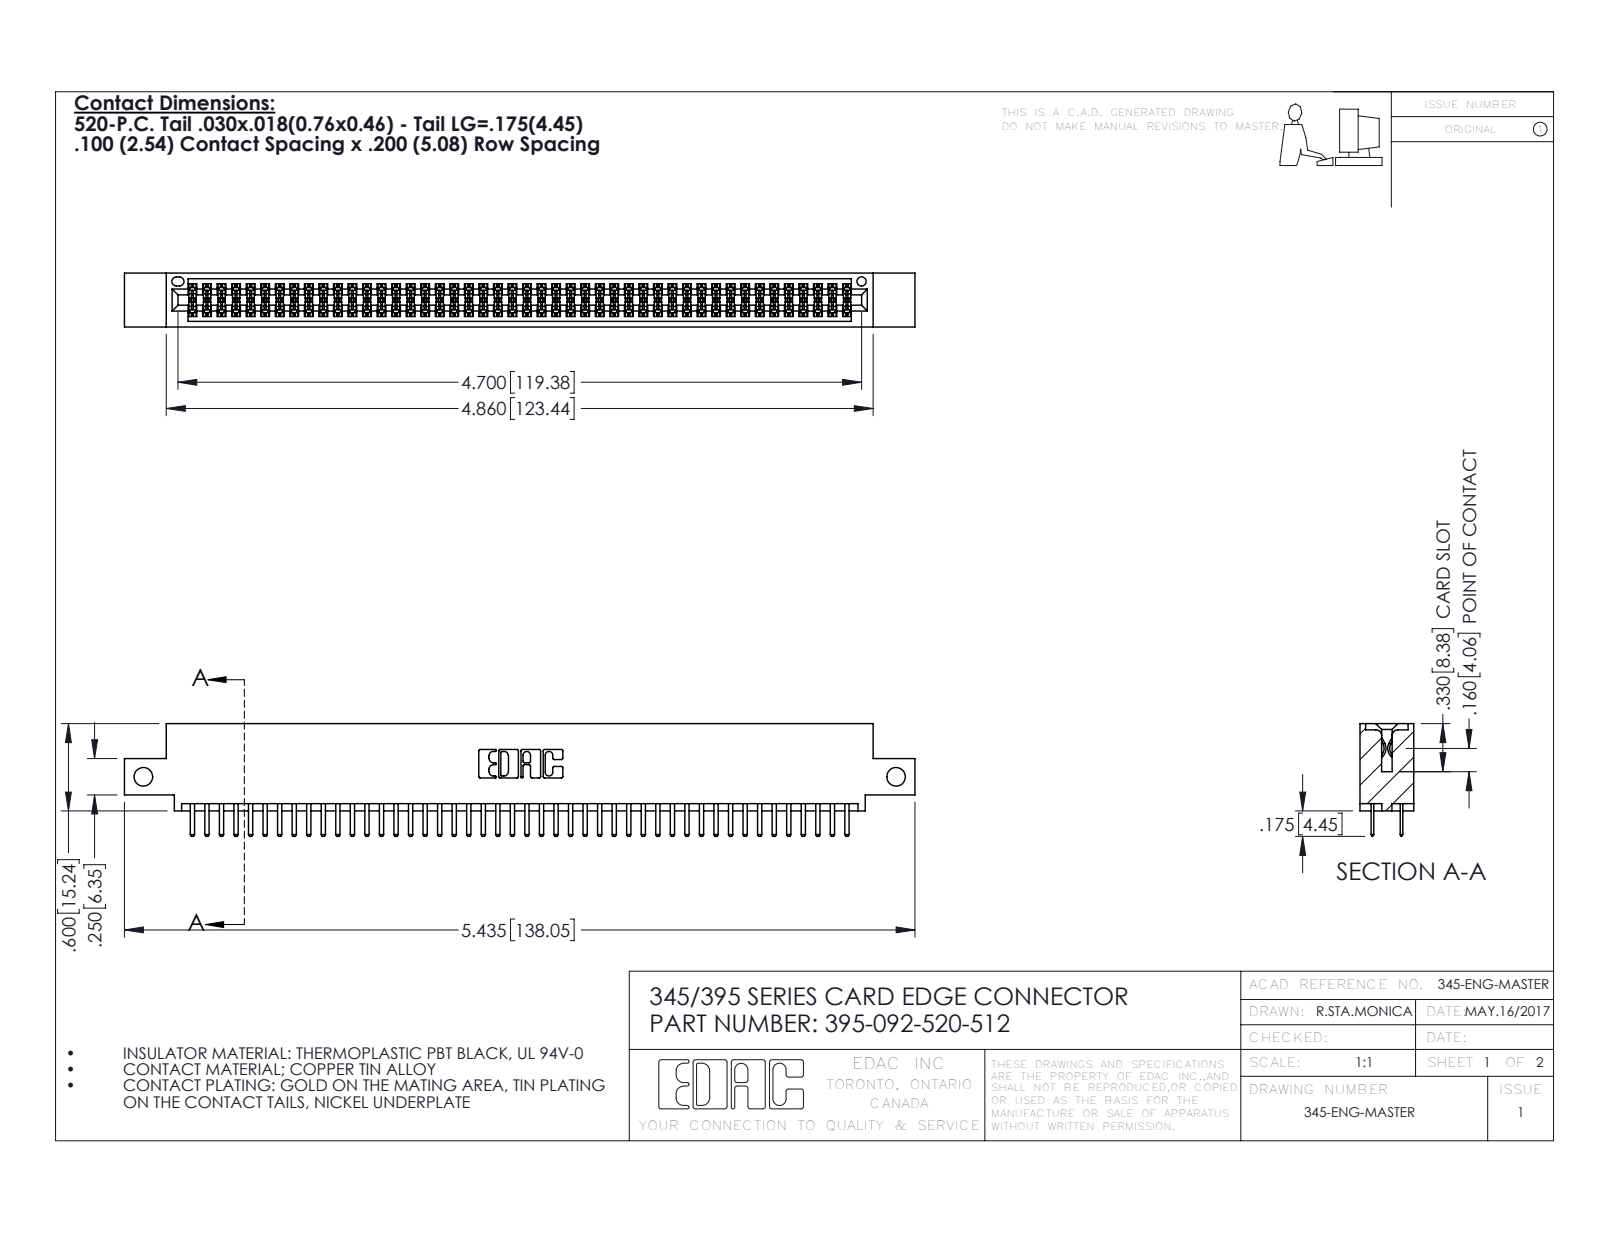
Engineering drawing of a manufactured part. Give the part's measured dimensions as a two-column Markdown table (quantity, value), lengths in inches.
| quantity | value |
| --- | --- |
| part name | 345 Part_0.110 Offset - Side Mount; 345-292-001_345-293-120; 395-092-520-512 |
| STEP written by | SolidWorks 2016 (CONFIG_CONTROL_DESIGN) |
| units | inches |
| bodies | 93 solids, 5098 faces (3304 planar, 1794 cylindrical, 0 other) |
| overall size | 5.435 × 0.775 × 0.37 |
| volume | 0.808 in³ |
| surface area | 30.27 in² |
| round holes (diameter × count) | 0.128 × 2, 0.064 × 1 |
| partial cylindrical surfaces (radius × count) | 0.006 × 138, 0.01 × 96, 0.01 × 22, 0.007 × 6, 0.031 × 6, 0.026 × 3, 0.014 × 2, 0.019 × 2 |
| main face-to-face distances | 0.298, 0.072, 0.2, 0.37, 0.098, 0.272, 0.025, 0.225, 0.022, 0.072 |
| hole center spacings | 5.175 |
